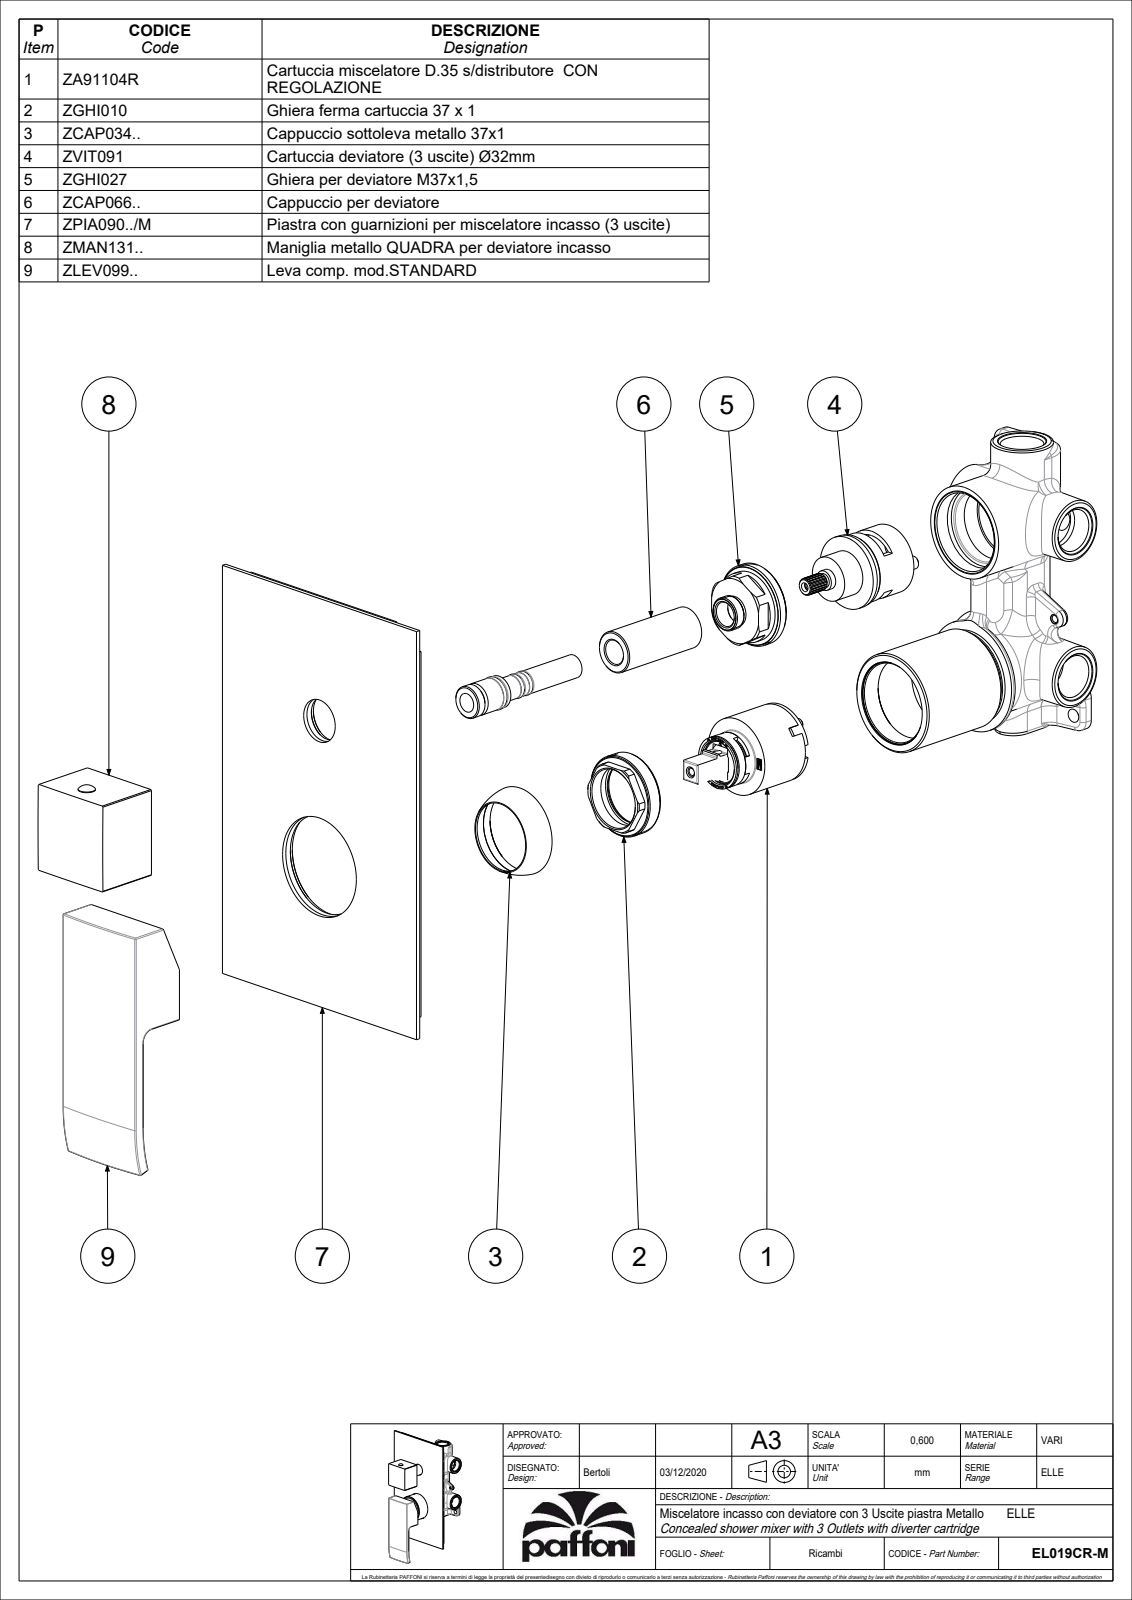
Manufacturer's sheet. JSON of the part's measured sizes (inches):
{"part_name": "EL018CRM", "step_written_by": "CREO PARAMETRIC BY PTC INC, 2020044 (CONFIG_CONTROL_DESIGN)", "units": "inches", "bodies": {"solids": 1, "faces": 149, "planar": 47, "cylindrical": 58, "other": 44}, "overall_size": [8.428, 4.724, 1.984], "volume_in3": 10.35, "surface_area_in2": 119.6, "round_holes": [[0.118, 1], [0.217, 1], [0.307, 1]], "round_bosses_or_shafts": [[0.299, 2], [1.764, 1], [0.736, 1], [0.197, 1]], "partial_cylinders_radius": [[0.059, 14], [0.02, 10], [0.079, 4], [11.811, 2], [1.102, 1]], "face_to_face_distances": [0.079, 1.575, 1.673, 0.098, 1.772, 0.783, 0.705, 1.783, 1.705, 1]}
